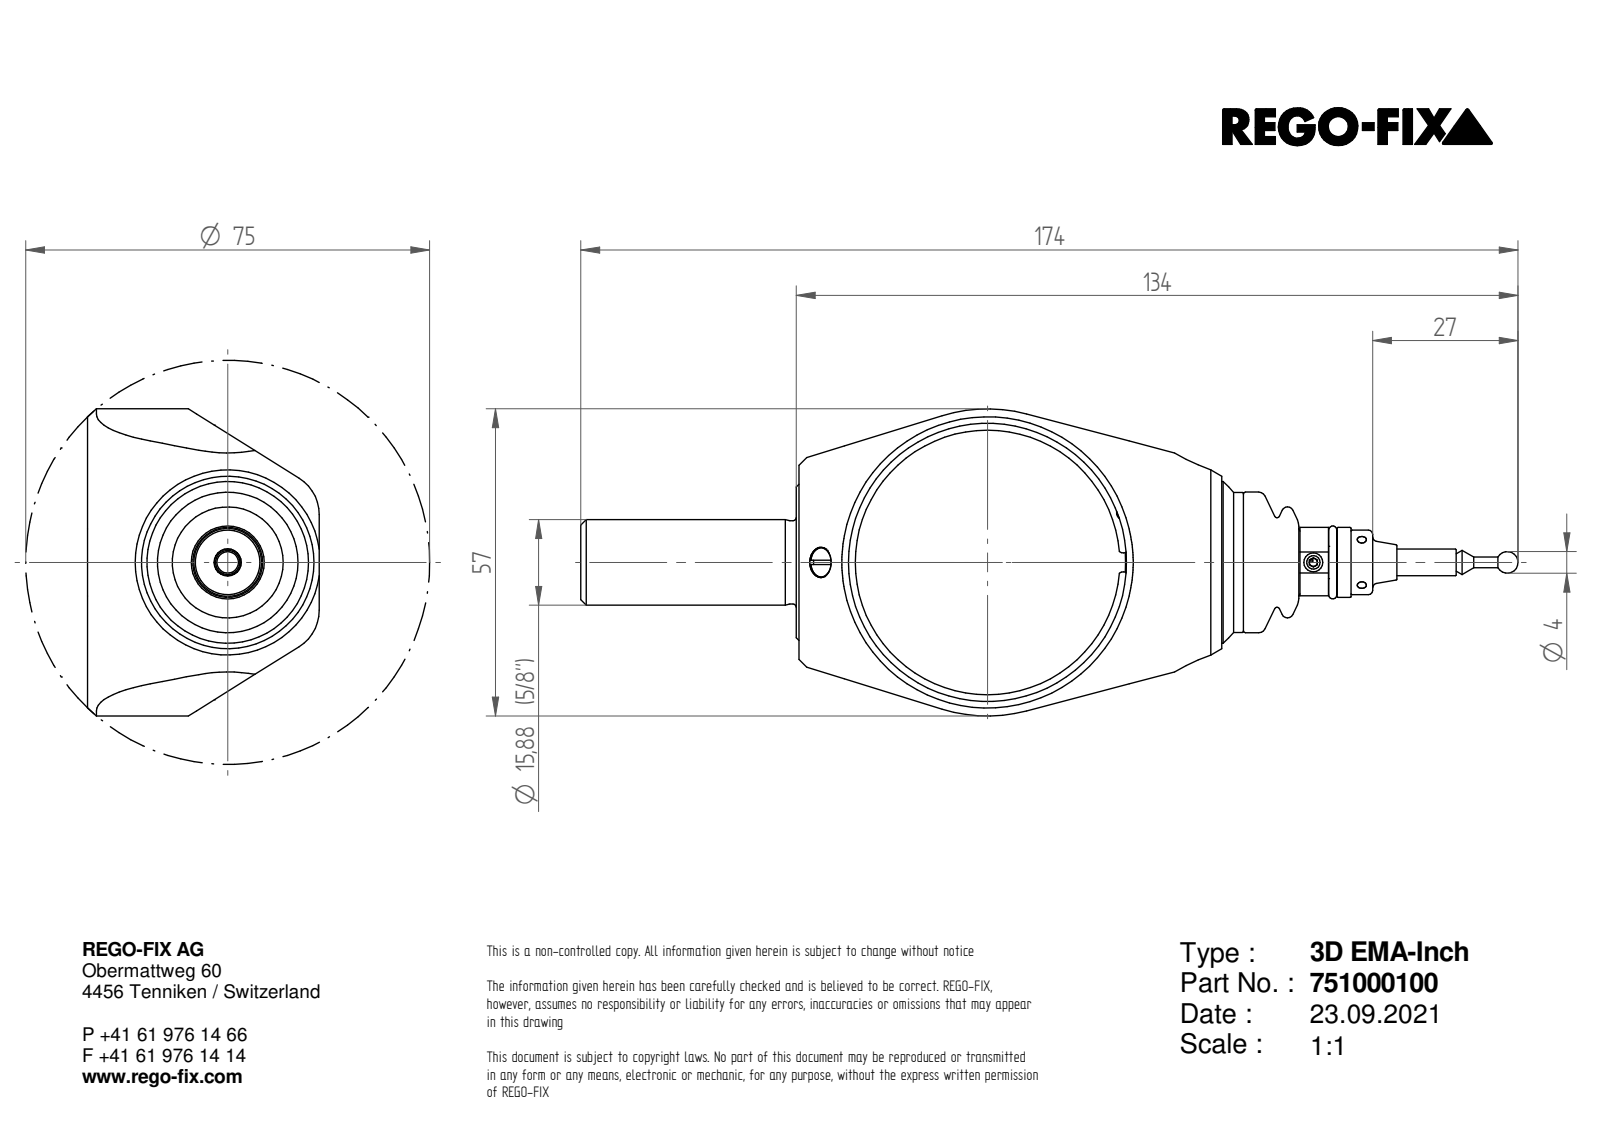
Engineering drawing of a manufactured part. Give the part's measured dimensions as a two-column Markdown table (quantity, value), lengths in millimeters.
| quantity | value |
| --- | --- |
| part name | EMA-only volume |
| STEP written by | ST-DEVELOPER v16.7 (AUTOMOTIVE_DESIGN) |
| units | millimeters |
| bodies | 1 solid, 79 faces (28 planar, 25 cylindrical, 26 other) |
| overall size | 174 × 57 × 43.22 |
| volume | 151 863 mm³ |
| surface area | 18 264 mm² |
| round bosses / shafts (diameter × count) | 30 × 1, 29 × 1, 26.1 × 1, 26 × 1, 20.6 × 1, 16 × 1, 13 × 1, 12.4 × 1 |
| partial cylindrical surfaces (radius × count) | 1.86 × 8, 8 × 2, 19.88 × 2, 28.5 × 1 |
| main face-to-face distances | 43, 0.5, 40.5, 40, 78.5, 79, 119, 14.3, 92.8, 93.3 |
